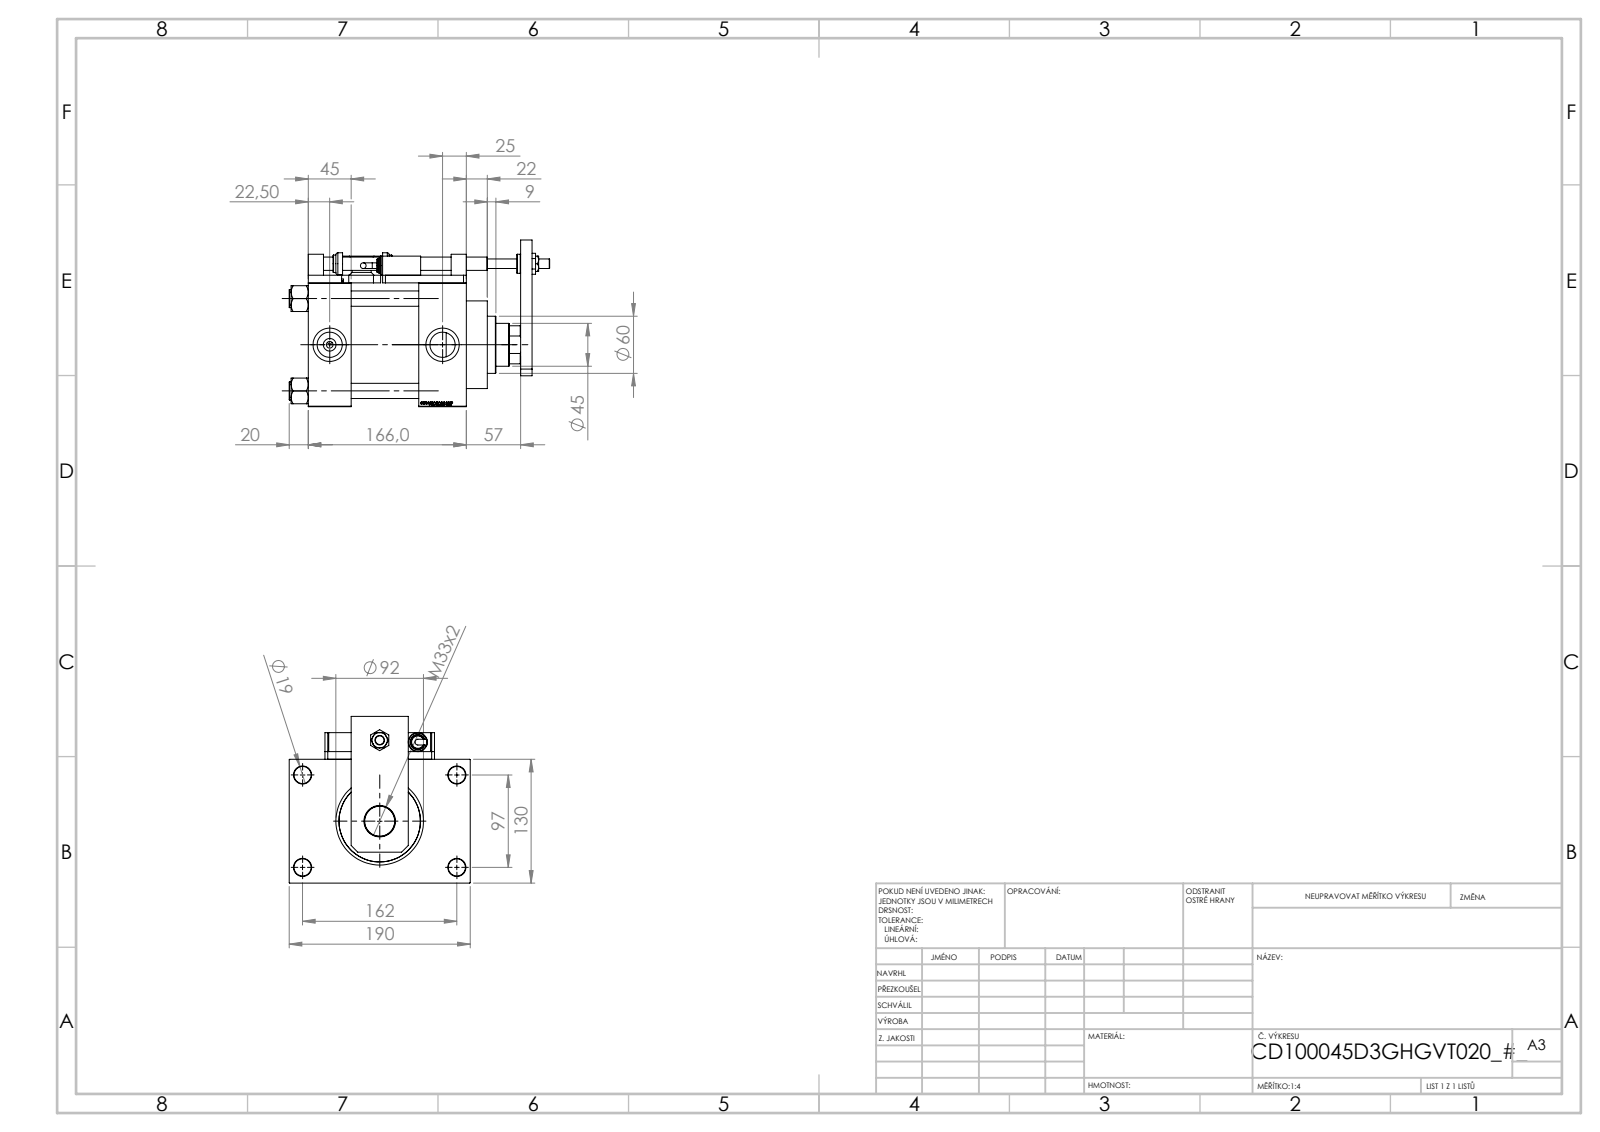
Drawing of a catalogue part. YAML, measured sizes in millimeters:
part_name: "V215CD_SWITCH_Q_TYC; Zatka_pro_OIL_PORT; V215CD_D_TYCINKA; V215CD_SWITCH_Q_PODLOZKA_BACK (+7 more)"
step_written_by: "SolidWorks 2019 (CONFIG_CONTROL_DESIGN)"
units: millimeters
bodies: {solids: 26, faces: 1480, planar: 714, cylindrical: 167, other: 599}
overall_size: [273.5, 190, 175]
volume: 2905000
surface_area: 459011
round_holes:
  - {diameter: 8.5, count: 4}
  - {diameter: 13.5, count: 4}
  - {diameter: 16, count: 4}
  - {diameter: 18, count: 4}
  - {diameter: 26.44, count: 4}
  - {diameter: 35, count: 4}
  - {diameter: 7, count: 3}
  - {diameter: 10, count: 1}
  - {diameter: 14, count: 1}
  - {diameter: 31.5, count: 1}
  - {diameter: 33, count: 1}
  - {diameter: 45, count: 1}
round_bosses_or_shafts:
  - {diameter: 19, count: 4}
  - {diameter: 20, count: 3}
  - {diameter: 16, count: 2}
  - {diameter: 14, count: 2}
  - {diameter: 6, count: 2}
  - {diameter: 106, count: 1}
  - {diameter: 92, count: 1}
  - {diameter: 60, count: 1}
partial_cylinders:
  - {radius: 7.5, count: 4}
  - {radius: 22, count: 1}
face_to_face_distances: [130, 45, 121, 166, 71, 8, 116, 50, 138, 190]
hole_center_spacings: [32.55, 68.52, 94.41, 96.9, 102.27, 129.45, 161.73, 21.59]
